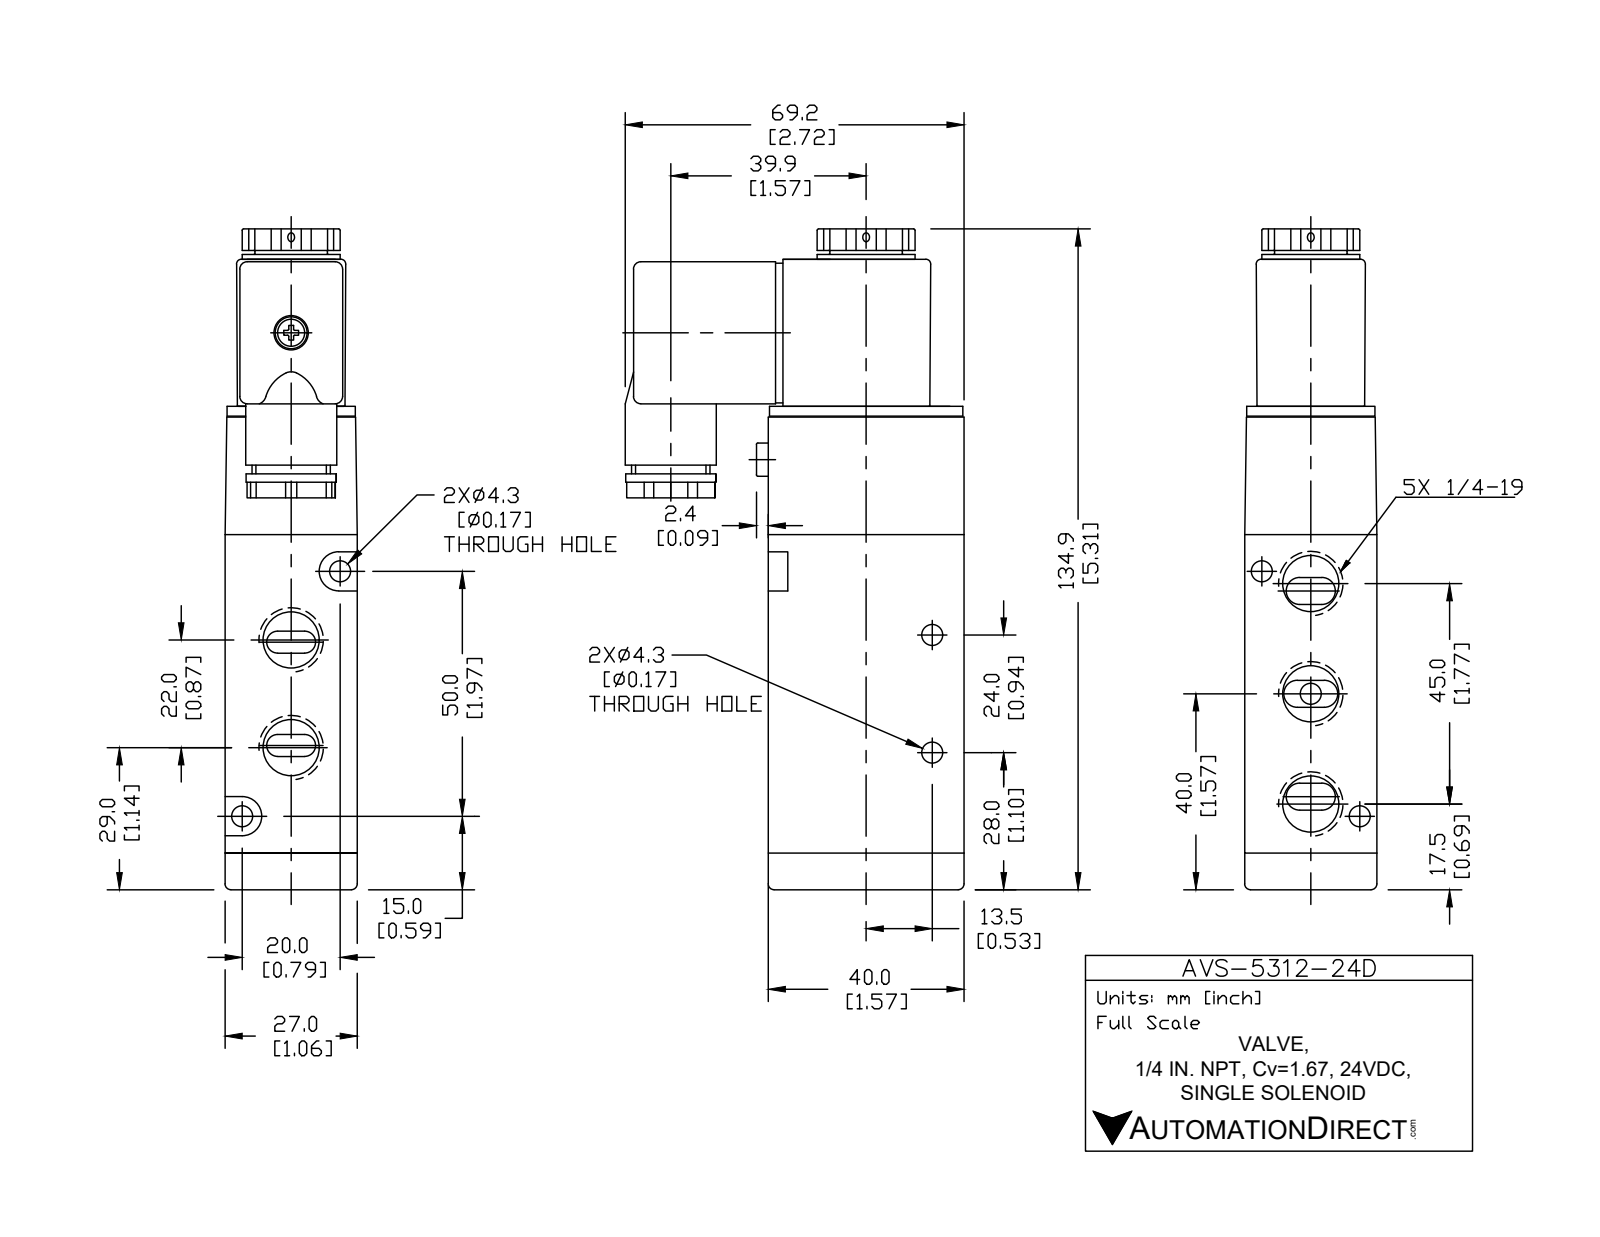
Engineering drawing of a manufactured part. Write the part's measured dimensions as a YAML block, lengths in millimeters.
part_name: "AVS-5312-24D"
step_written_by: "SolidWorks 2015 (CONFIG_CONTROL_DESIGN)"
units: millimeters
bodies: {solids: 4, faces: 192, planar: 88, cylindrical: 77, other: 27}
overall_size: [134.9, 69.2, 27]
volume: 140587
surface_area: 31964
round_holes:
  - {diameter: 11.13, count: 5}
  - {diameter: 4.3, count: 4}
  - {diameter: 9.3, count: 1}
round_bosses_or_shafts:
  - {diameter: 20, count: 1}
  - {diameter: 18.6, count: 1}
  - {diameter: 18.4, count: 1}
  - {diameter: 16, count: 1}
  - {diameter: 14.8, count: 1}
  - {diameter: 6.7, count: 1}
partial_cylinders:
  - {radius: 1.5, count: 12}
  - {radius: 1.54, count: 10}
  - {radius: 0.5, count: 8}
  - {radius: 1, count: 5}
  - {radius: 3, count: 2}
face_to_face_distances: [27, 65, 40, 24, 3, 7.5, 72.5, 21, 27.5, 29.5]
hole_center_spacings: [10.31, 11, 11.5, 17.2, 22.5, 26.93, 33.5, 37.36]
